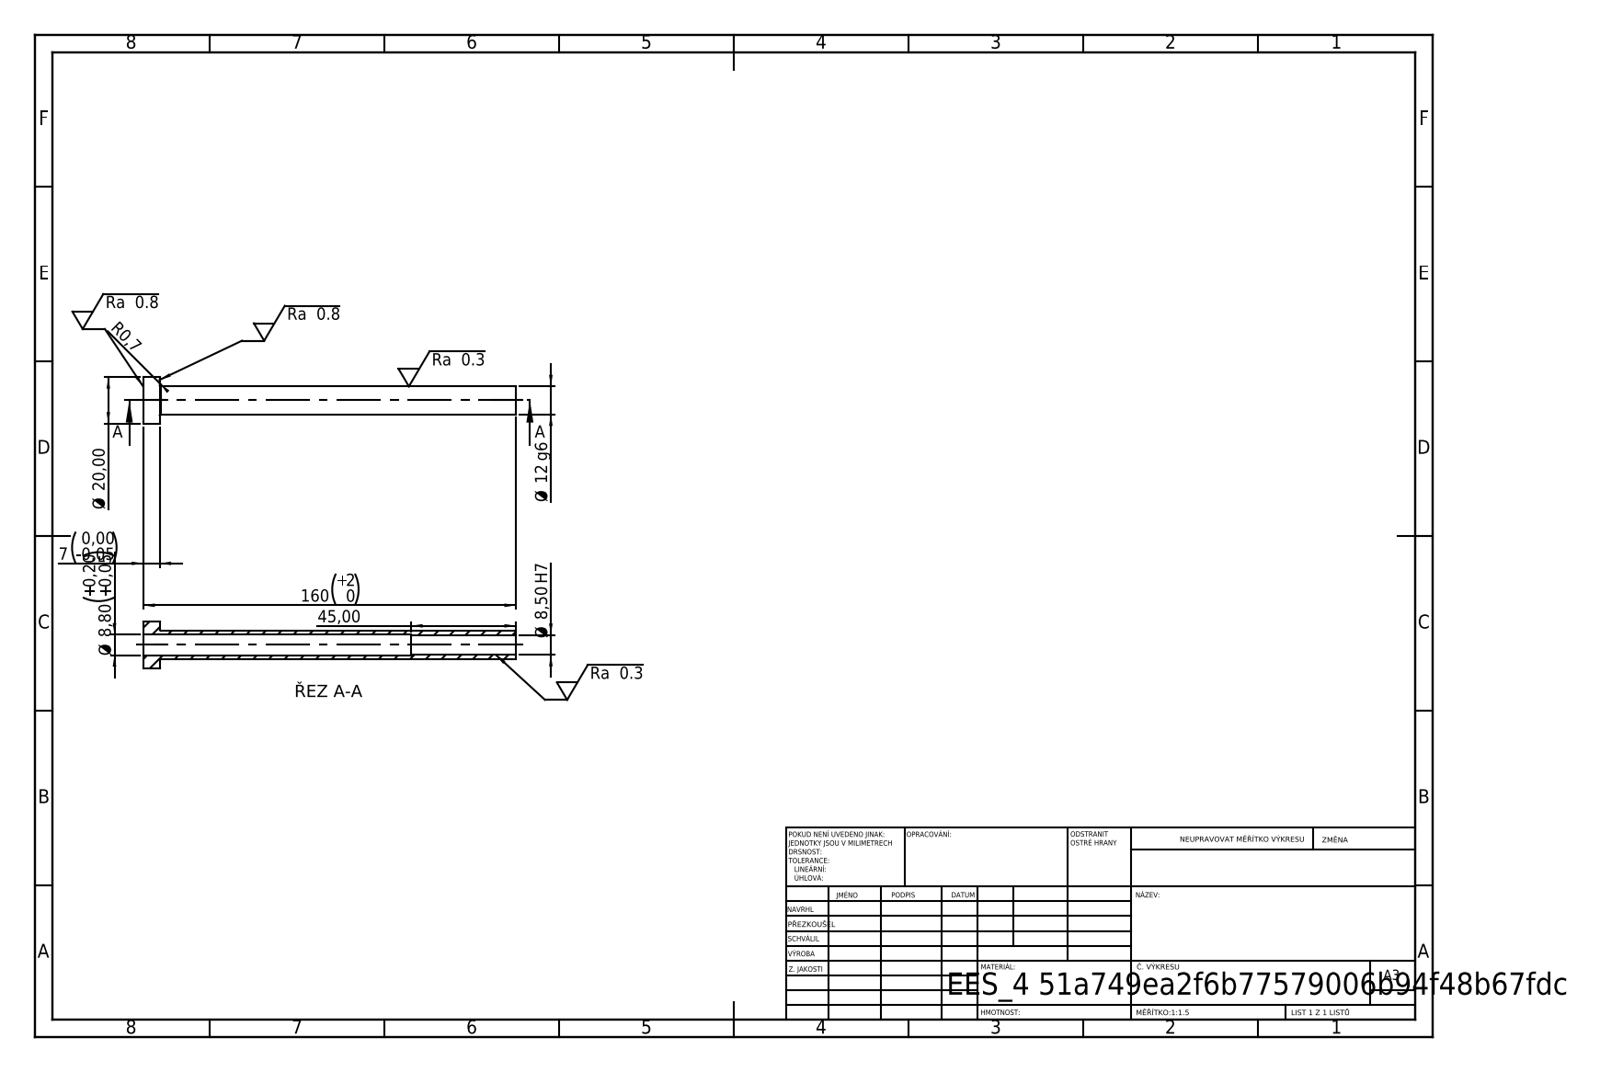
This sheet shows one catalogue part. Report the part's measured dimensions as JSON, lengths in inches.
{"step_written_by": "SolidWorks 2019 (CONFIG_CONTROL_DESIGN)", "units": "inches", "bodies": {"solids": 1, "faces": 14, "planar": 4, "cylindrical": 8, "other": 2}, "overall_size": [6.299, 0.787, 0.787], "volume_in3": 0.608, "surface_area_in2": 17.19, "round_holes": [[0.335, 1], [0.346, 1]], "round_bosses_or_shafts": [[0.787, 1], [0.472, 1]], "face_to_face_distances": [0.276, 6.299, 6.024, 4.528, 4.252, 1.772]}
